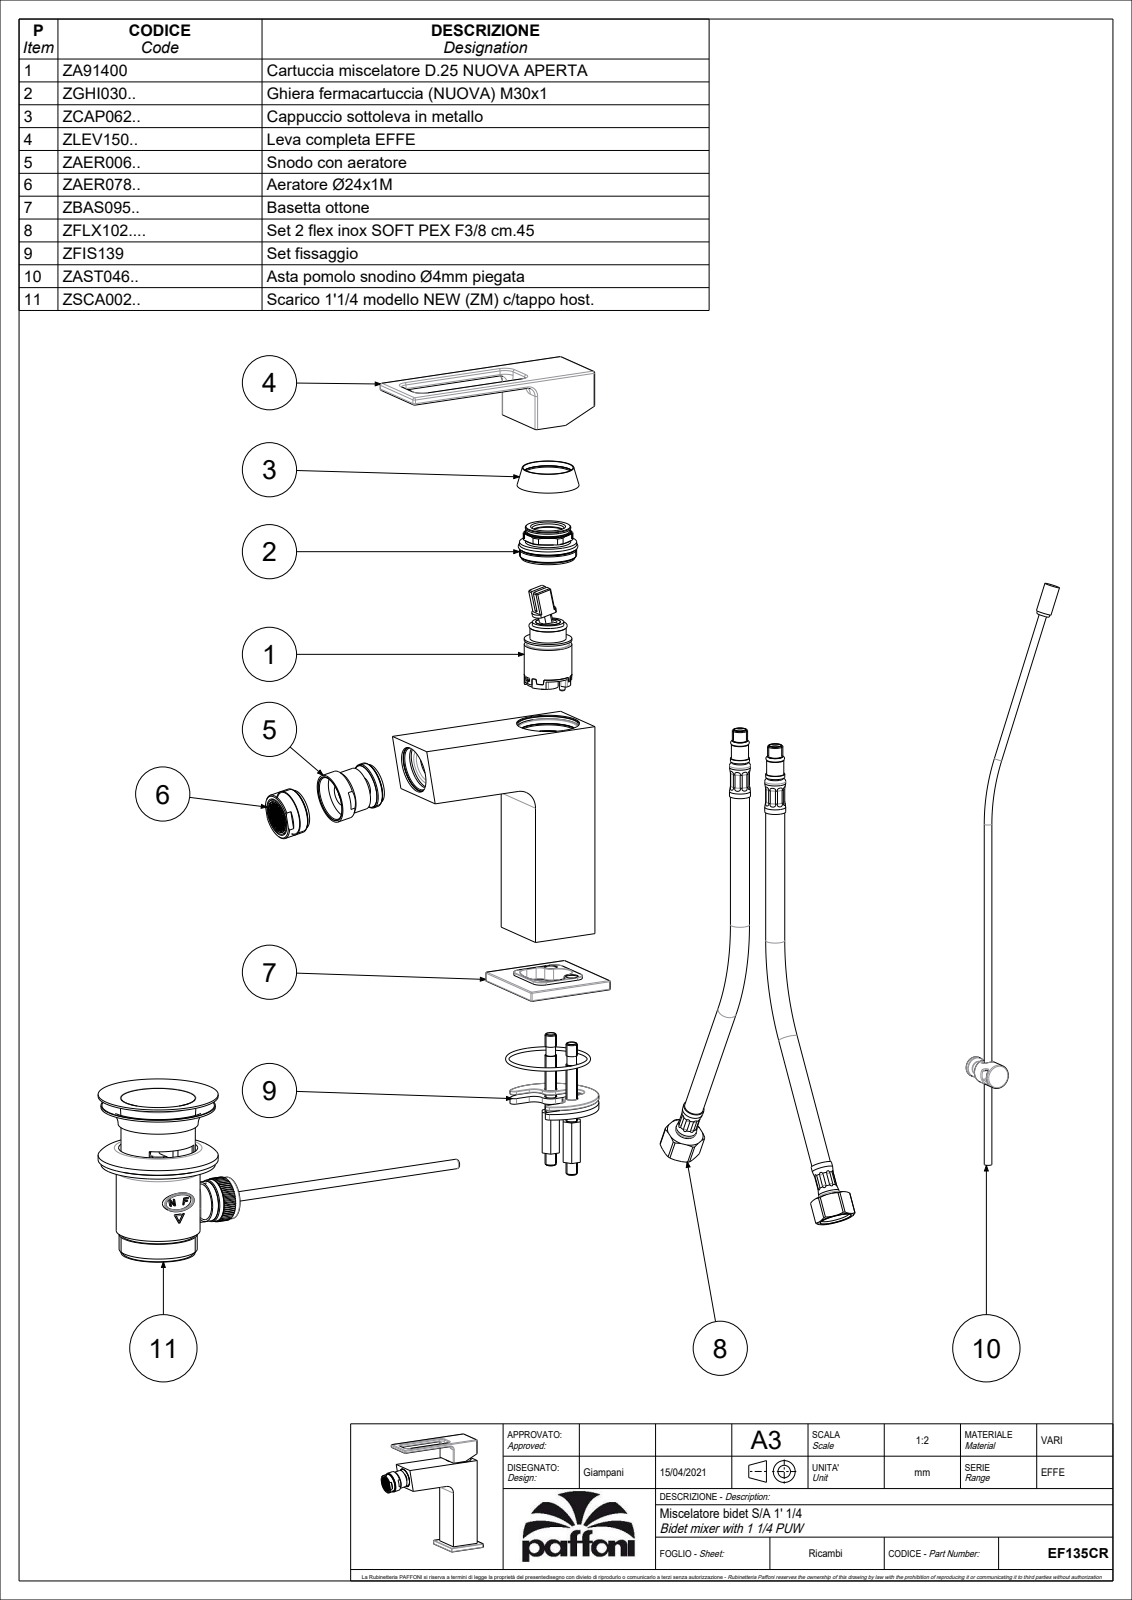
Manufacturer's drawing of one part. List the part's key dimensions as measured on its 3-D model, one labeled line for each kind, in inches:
Part name (STEP PRODUCT): EF135CR
STEP written by: CREO PARAMETRIC BY PTC INC, 2020044 (CONFIG_CONTROL_DESIGN)
Units: inches
Bodies: 9 solids, 2070 faces (1583 planar, 300 cylindrical, 187 other)
Overall size (bounding box): 5.731 × 5.722 × 1.89
Volume: 7.67 in³ · Surface area: 124.8 in²
Round holes (diameter × count): ⌀0.217 ×3, ⌀0.244 ×2, ⌀0.906 ×2, ⌀0.118 ×1, ⌀0.165 ×1, ⌀0.177 ×1, ⌀0.197 ×1, ⌀0.307 ×1, ⌀0.315 ×1, ⌀0.61 ×1, ⌀0.63 ×1, ⌀0.669 ×1
Round bosses / shafts (diameter × count): ⌀0.394 ×3, ⌀0.315 ×3, ⌀0.433 ×2, ⌀0.354 ×2, ⌀0.256 ×2, ⌀1.646 ×1, ⌀1.016 ×1, ⌀0.945 ×1
Partial cylindrical surfaces — rounded edges, fillets, slot ends (radius × count): R0.039 ×62, R0.118 ×28, R0.02 ×14, R0.197 ×11, R0.059 ×8, R0.01 ×6, R0.157 ×6, R0.138 ×2
Main face-to-face distances: 0.118, 1.299, 1.417, 1.181, 1.024, 1.106, 1.142, 2.247, 0.354, 3.484
Hole centre spacings: 0.449, 0.535, 0.433, 0.866
